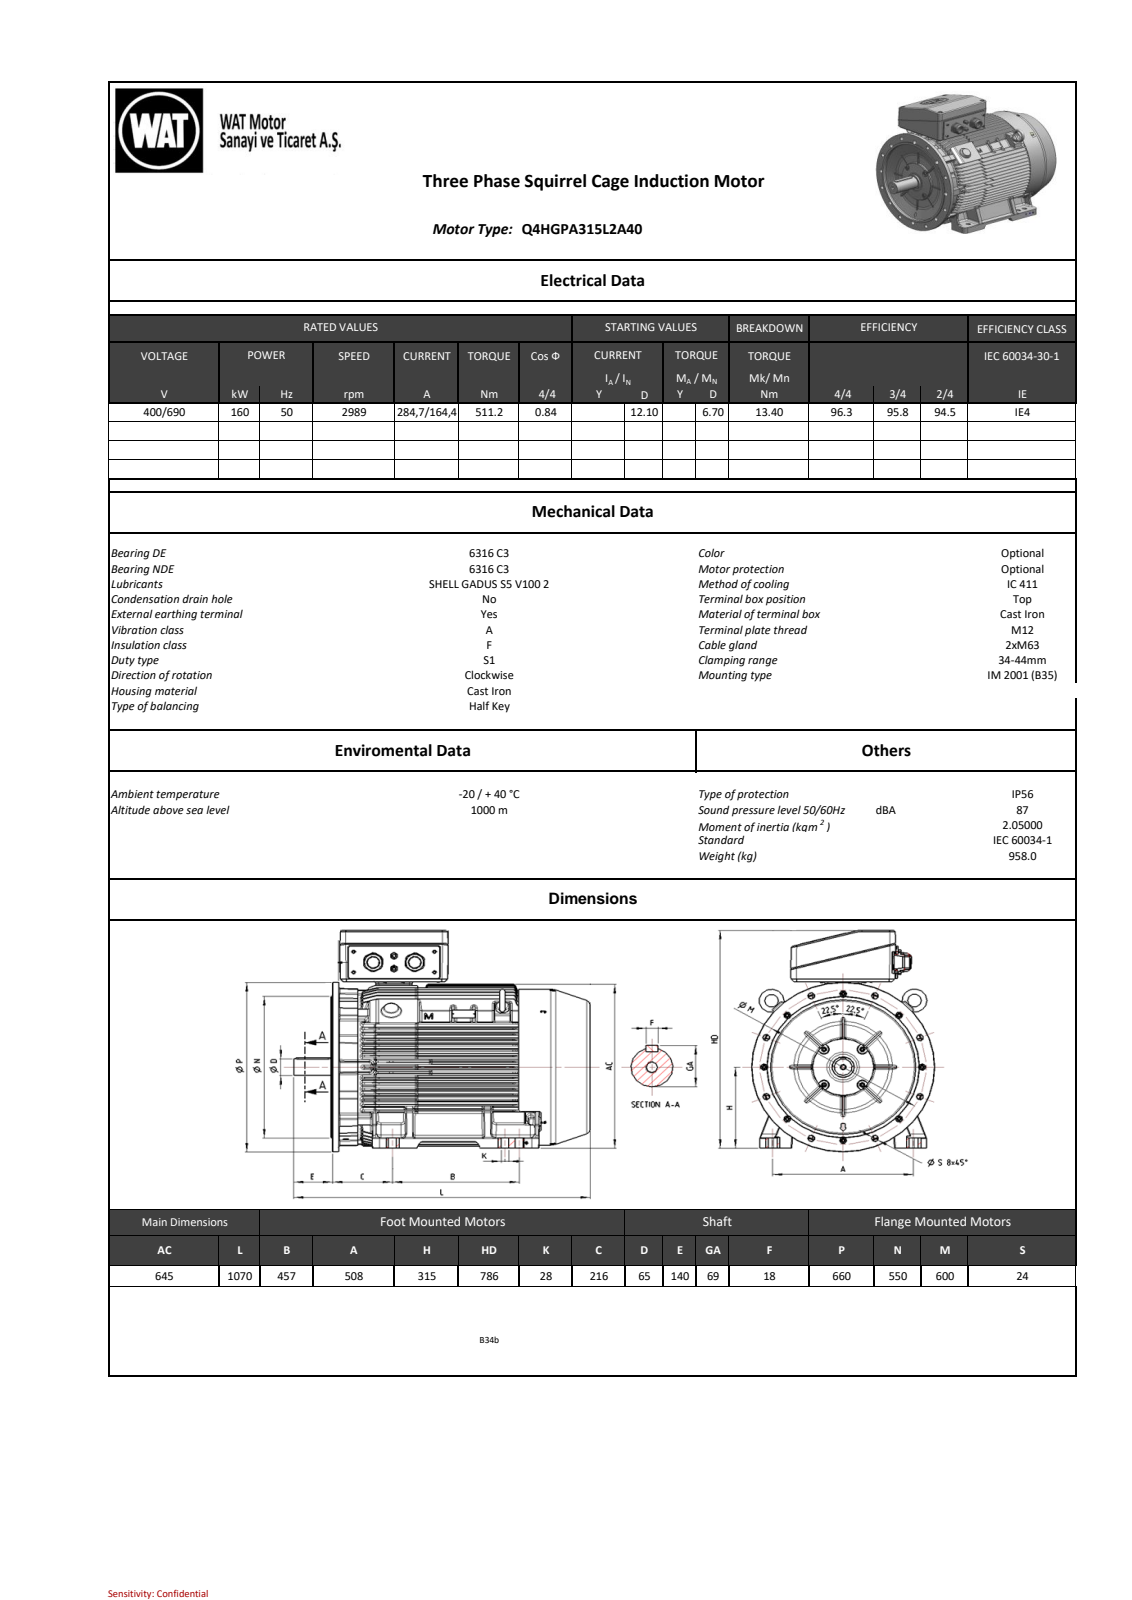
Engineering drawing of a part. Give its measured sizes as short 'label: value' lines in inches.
name: 26009910674F4pxh
written by: SIEMENS PLM Software NX 11.0 (AUTOMOTIVE_DESIGN)
unit: in
bodies: 0 solids, 6808 faces (3091 planar, 1414 cylindrical, 2303 other)
size: 42.126 × 33.952 × 25.984
holes: 8× ⌀0.945, 8× ⌀1.024, 4× ⌀0.787, 3× ⌀0.315, 3× ⌀0.335, 3× ⌀0.354, 2× ⌀0.209, 2× ⌀0.394, 2× ⌀0.472, 2× ⌀0.709, 2× ⌀1.732, 2× ⌀1.748
bosses: 8× ⌀0.63, 7× ⌀0.394, 4× ⌀0.787, 2× ⌀2.551, 2× ⌀1.969, 1× ⌀25.984, 1× ⌀23.898, 1× ⌀22.244
rounds: 625× R0.236, 111× R0.118, 66× R0.059, 59× R0.082, 54× R0.103, 37× R0.031, 34× R0.591, 26× R0.394
face distances: 4.606, 0.819, 10.38, 0.815, 12.014, 1.641, 9.557, 0.822, 8.738, 11.195
hole spacings: 19.153, 3.113, 5.906, 4.53, 4.531, 8.588, 11.811, 12.805
